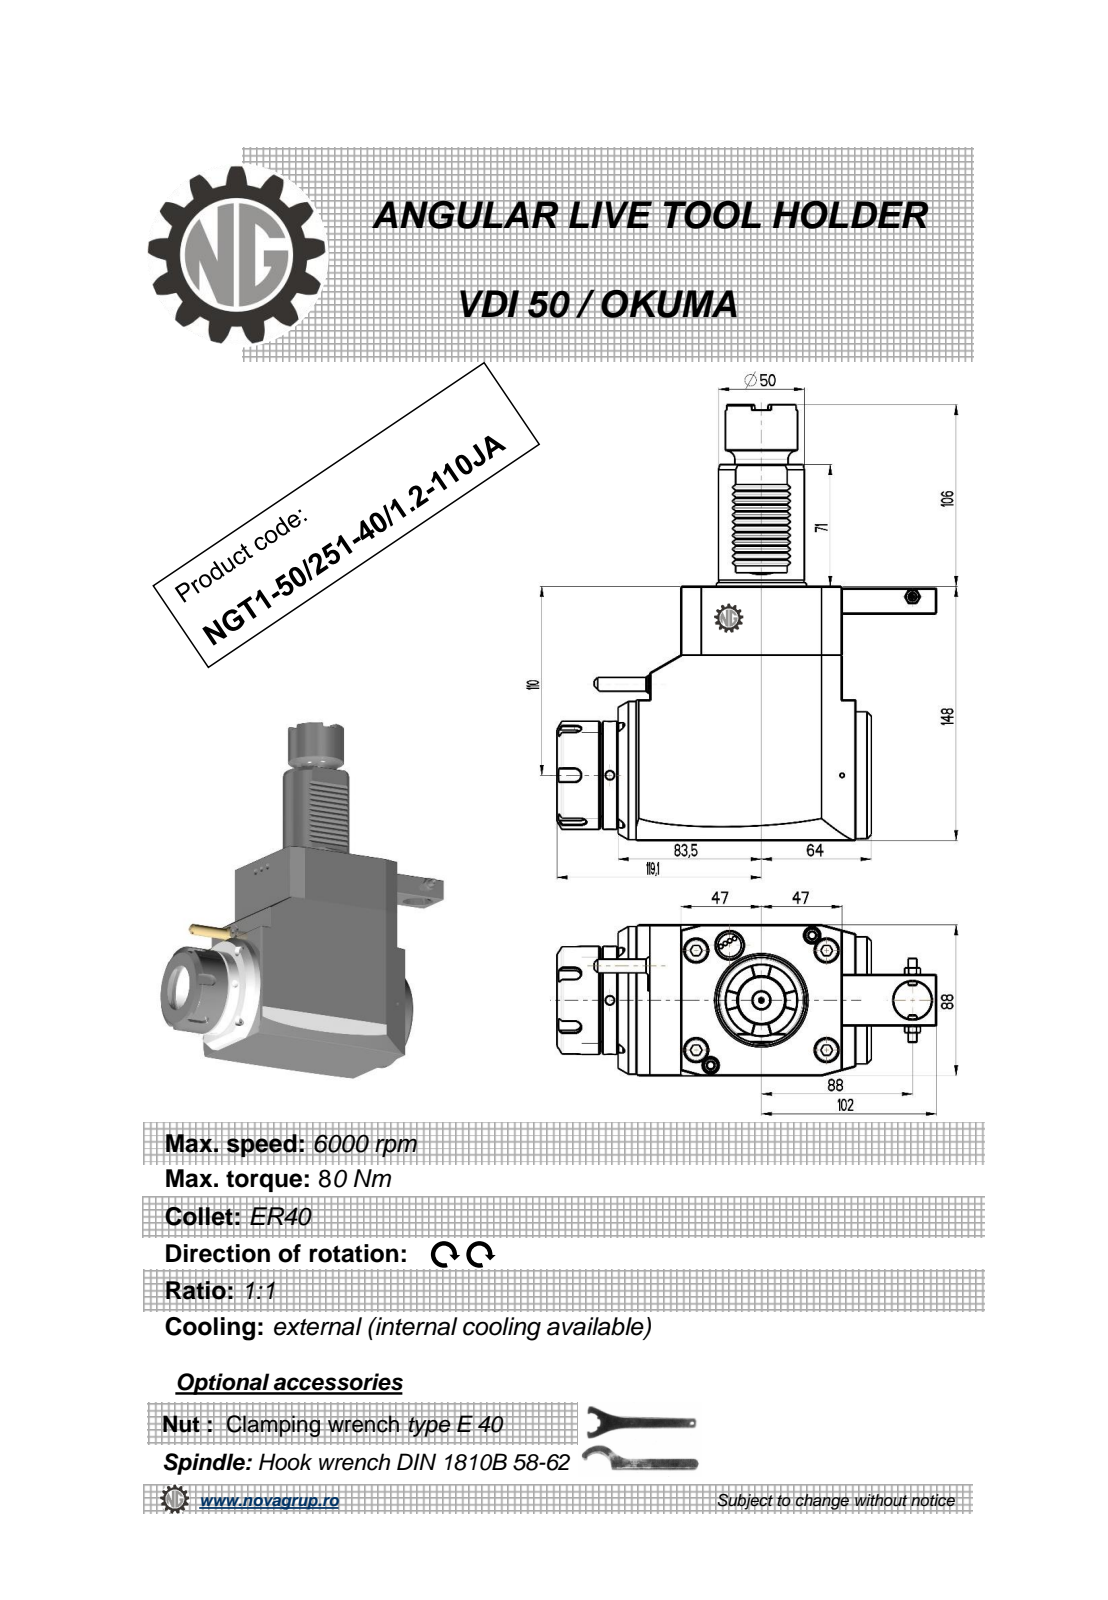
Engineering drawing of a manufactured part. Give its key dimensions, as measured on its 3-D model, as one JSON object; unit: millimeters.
{"part_name": "NGT1_50_251_40_1_2_110JA", "step_written_by": "PRO/ENGINEER BY PARAMETRIC TECHNOLOGY CORPORATION, 2010280 (CONFIG_CONTROL_DESIGN)", "units": "millimeters", "bodies": {"solids": 1, "faces": 492, "planar": 228, "cylindrical": 103, "other": 161}, "overall_size": [254, 221.1, 88], "volume_mm3": 1870000, "surface_area_mm2": 122065, "round_holes": [[5, 3], [3, 1], [4.2, 1], [4.5, 1], [9.5, 1], [12, 1], [22, 1], [28, 1], [33.5, 1]], "round_bosses_or_shafts": [[5, 2], [86, 1], [74, 1], [63, 1], [51, 1], [50, 1], [42, 1], [31, 1]], "partial_cylinders_radius": [[0.26, 12], [0.3, 12], [0.2, 6], [3.75, 5], [2.5, 1]], "face_to_face_distances": [88, 148, 147.5, 17, 8, 111, 94, 9, 36.5, 130.5], "hole_center_spacings": [52.46, 56.65, 88, 88.25, 101.5, 176.25]}
